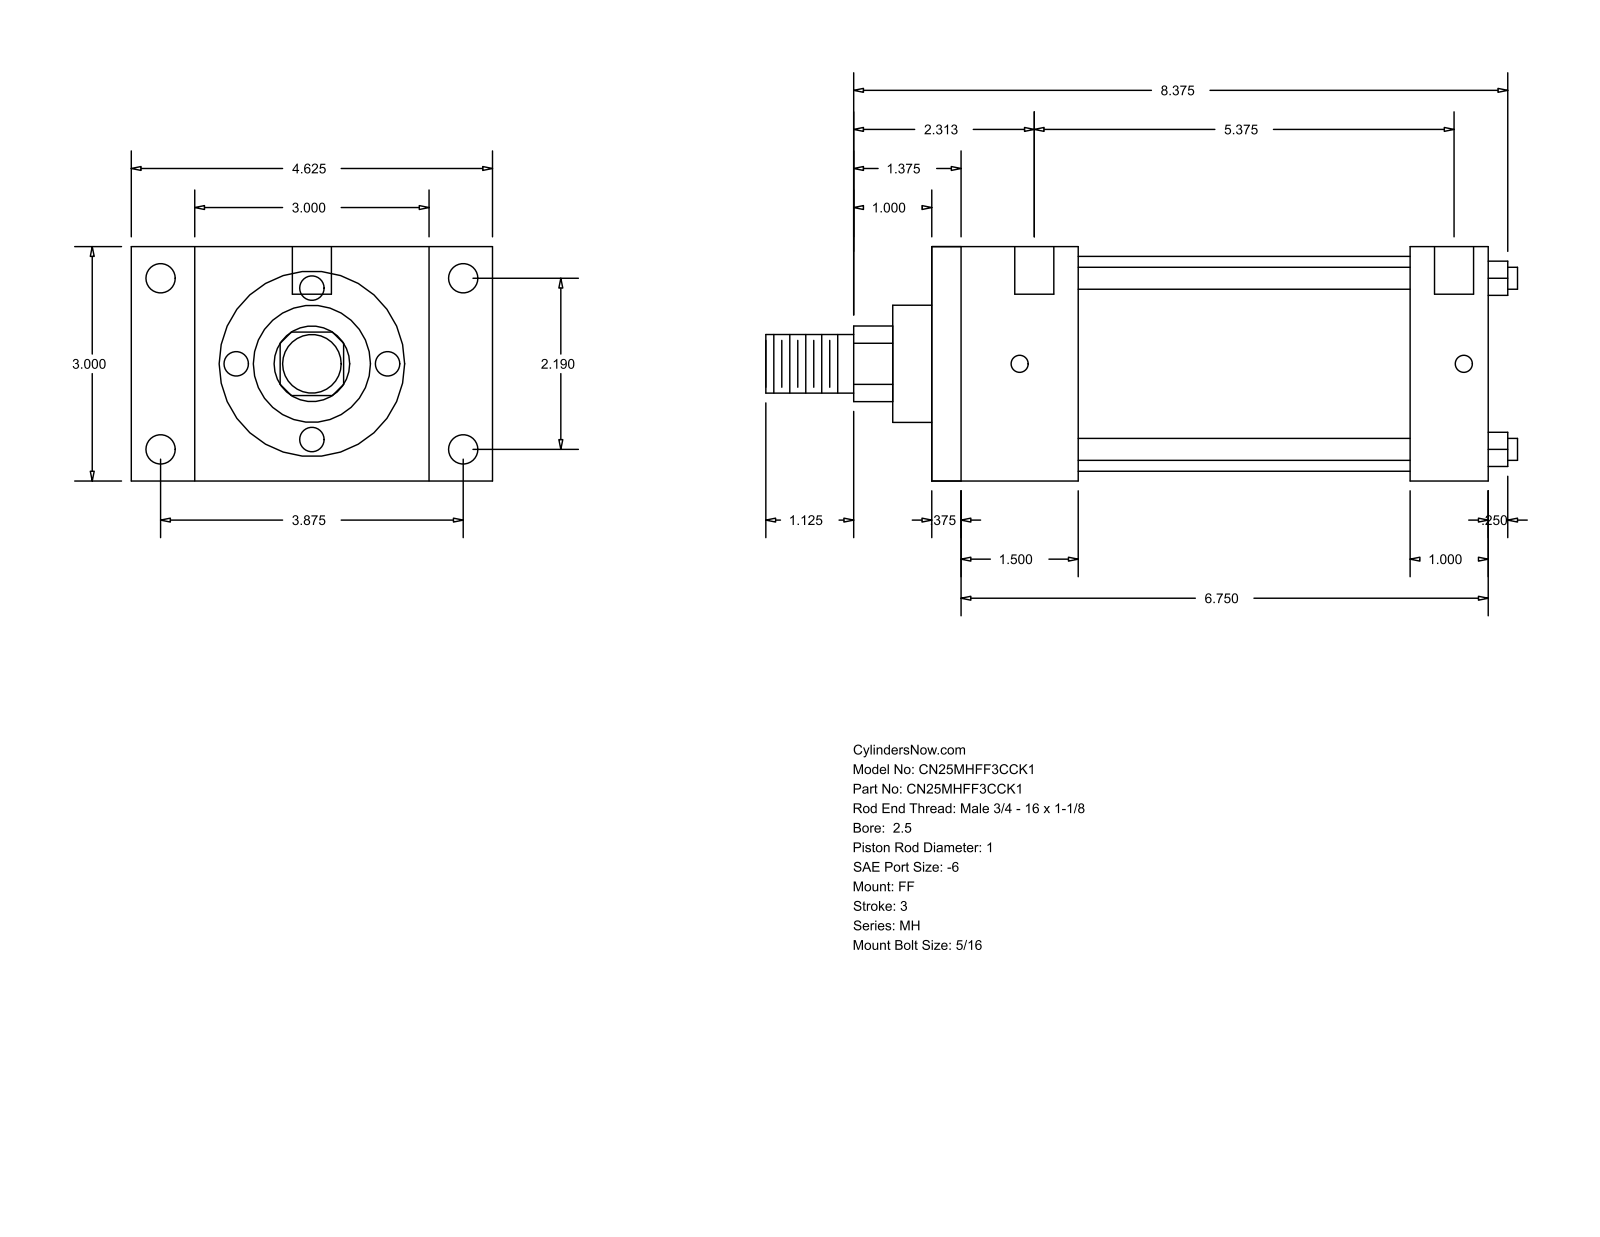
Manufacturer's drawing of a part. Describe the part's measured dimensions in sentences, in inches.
The part is named "MH_FF__0250_1". Its 3-D file was written by "GSSL Pune (CONFIG_CONTROL_DESIGN)". It is 0 solids with 92 faces: 64 planar, 28 cylindrical and 0 other. Overall it measures 9.625 by 4.625 by 3 inches. Round holes: 4 of diameter 0.219, 4 of diameter 0.375, 2 of diameter 0.5. Round bosses or shafts: 4 of diameter 0.281, 1 of diameter 2.75, 1 of diameter 1.5, 1 of diameter 1, 1 of diameter 0.75. Partial cylindrical surfaces (rounded edges, fillets, slot ends): 1 of radius 0.484. The main face-to-face distances are 3, 7.125, 0.375, 6.75, 1.875, 6.125, 1.5, 5.75, 4.25, 5.25. The hole center spacings are 2.19, 3.875, 4.451, 5.687, 0.125, 0.187, 5.375, 5.5.
